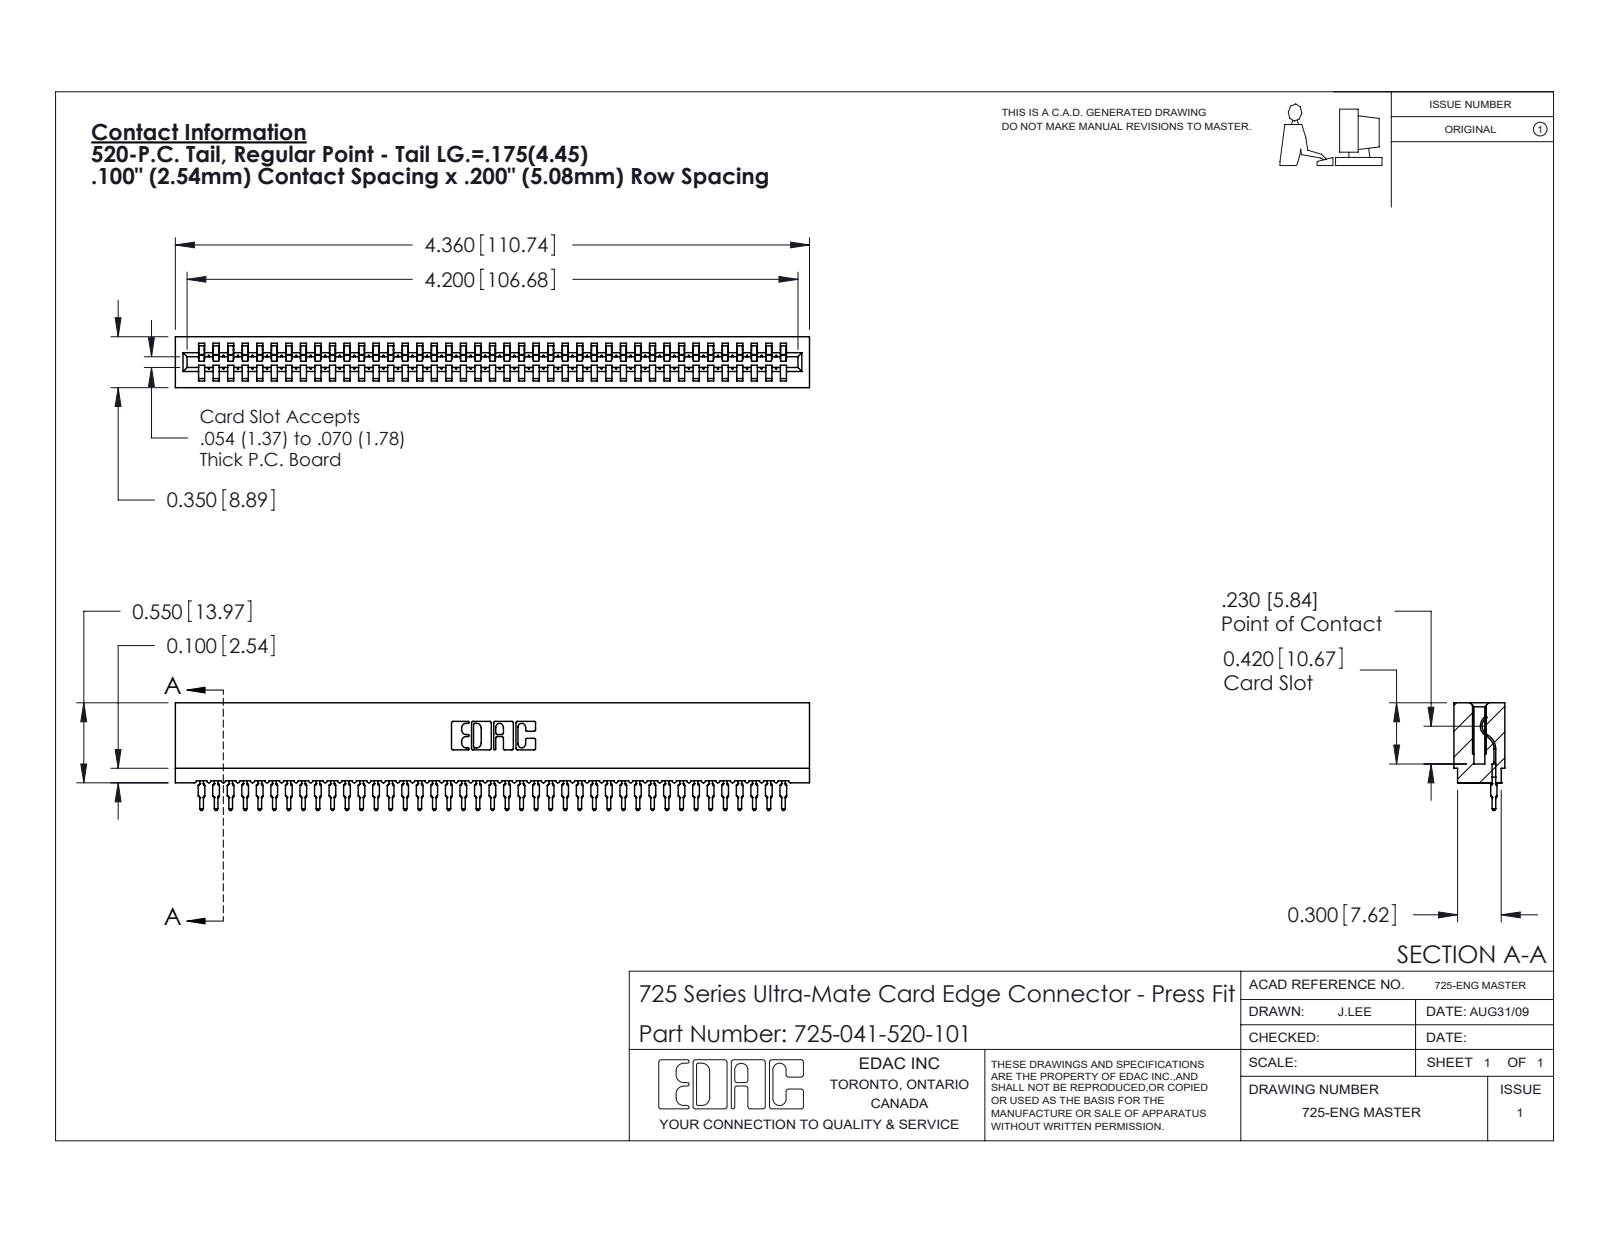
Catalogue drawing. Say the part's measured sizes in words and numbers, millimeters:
The part is named "745-292-001_520; 725 Part_Insulator Option - 01; 725-041-520-101". Its 3-D file was written by "SolidWorks 2020 (CONFIG_CONTROL_DESIGN)". It is 42 solids with 4687 faces: 2802 planar, 819 cylindrical and 1066 other. Overall it measures 110.7 by 18.8 by 8.9 millimeters. Its volume is 8 360 cubic millimeters and its surface area 15 830 square millimeters. Partial cylindrical surfaces (rounded edges, fillets, slot ends): 82 of radius 0.4, 82 of radius 0.5, 22 of radius 0.3, 6 of radius 0.2, 6 of radius 0.8, 4 of radius 0.1, 4 of radius 0.3, 3 of radius 0.7. The main face-to-face distances are 8.9, 5.1, 2.5, 5.4, 3.5, 1.1, 7.7, 2.4, 4.2, 7.6.
